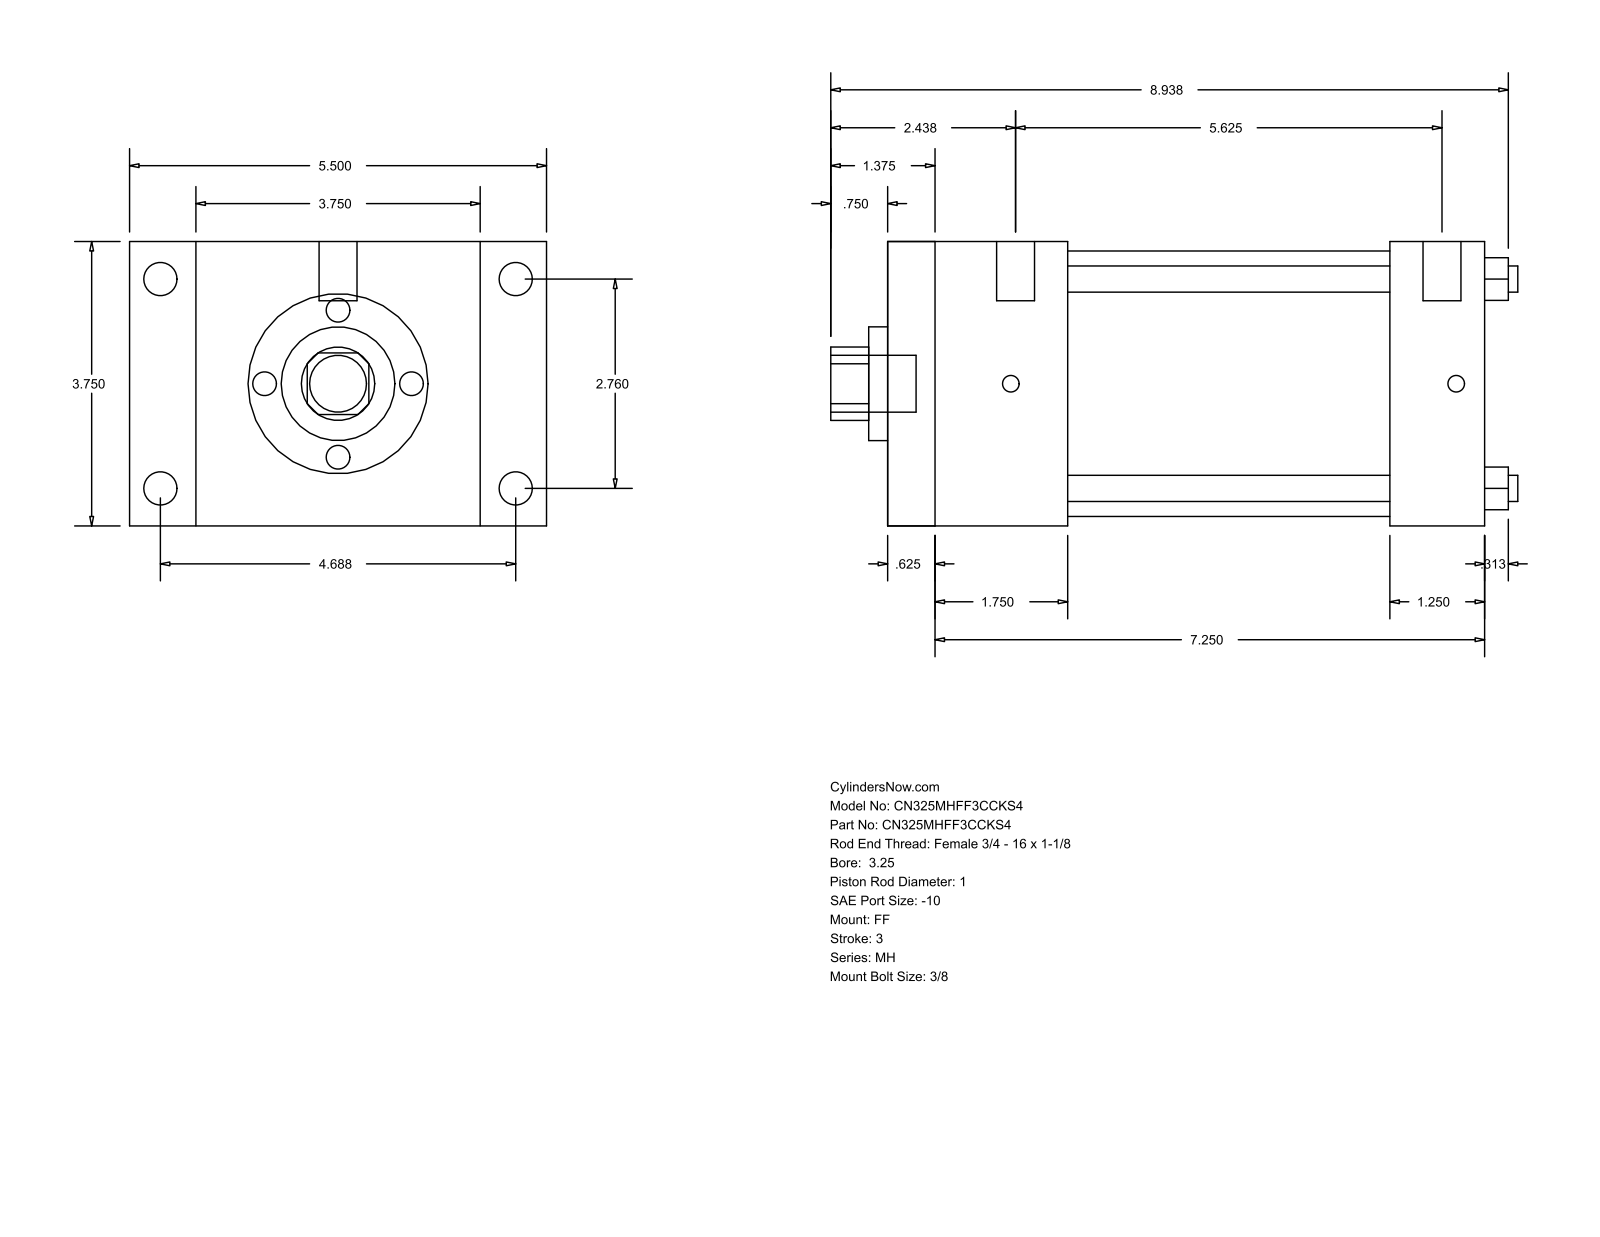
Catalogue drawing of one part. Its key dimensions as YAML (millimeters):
part_name: "MH_FF__0325_1"
step_written_by: "GSSL Pune (CONFIG_CONTROL_DESIGN)"
units: millimeters
bodies: {solids: 0, faces: 92, planar: 64, cylindrical: 28, other: 0}
overall_size: [230.19, 139.7, 95.25]
round_holes:
  - {diameter: 8.76, count: 4}
  - {diameter: 25.4, count: 1}
  - {diameter: 38.1, count: 1}
  - {diameter: 88.9, count: 1}
round_bosses_or_shafts:
  - {diameter: 11.13, count: 4}
  - {diameter: 5.56, count: 4}
  - {diameter: 12.7, count: 2}
  - {diameter: 19.05, count: 1}
partial_cylinders:
  - {radius: 12.29, count: 1}
face_to_face_distances: [95.24, 200.02, 15.87, 184.15, 22.23, 117.47, 168.27, 152.4, 31.75, 60.33]
hole_center_spacings: [49.57, 70.1, 99.14]
